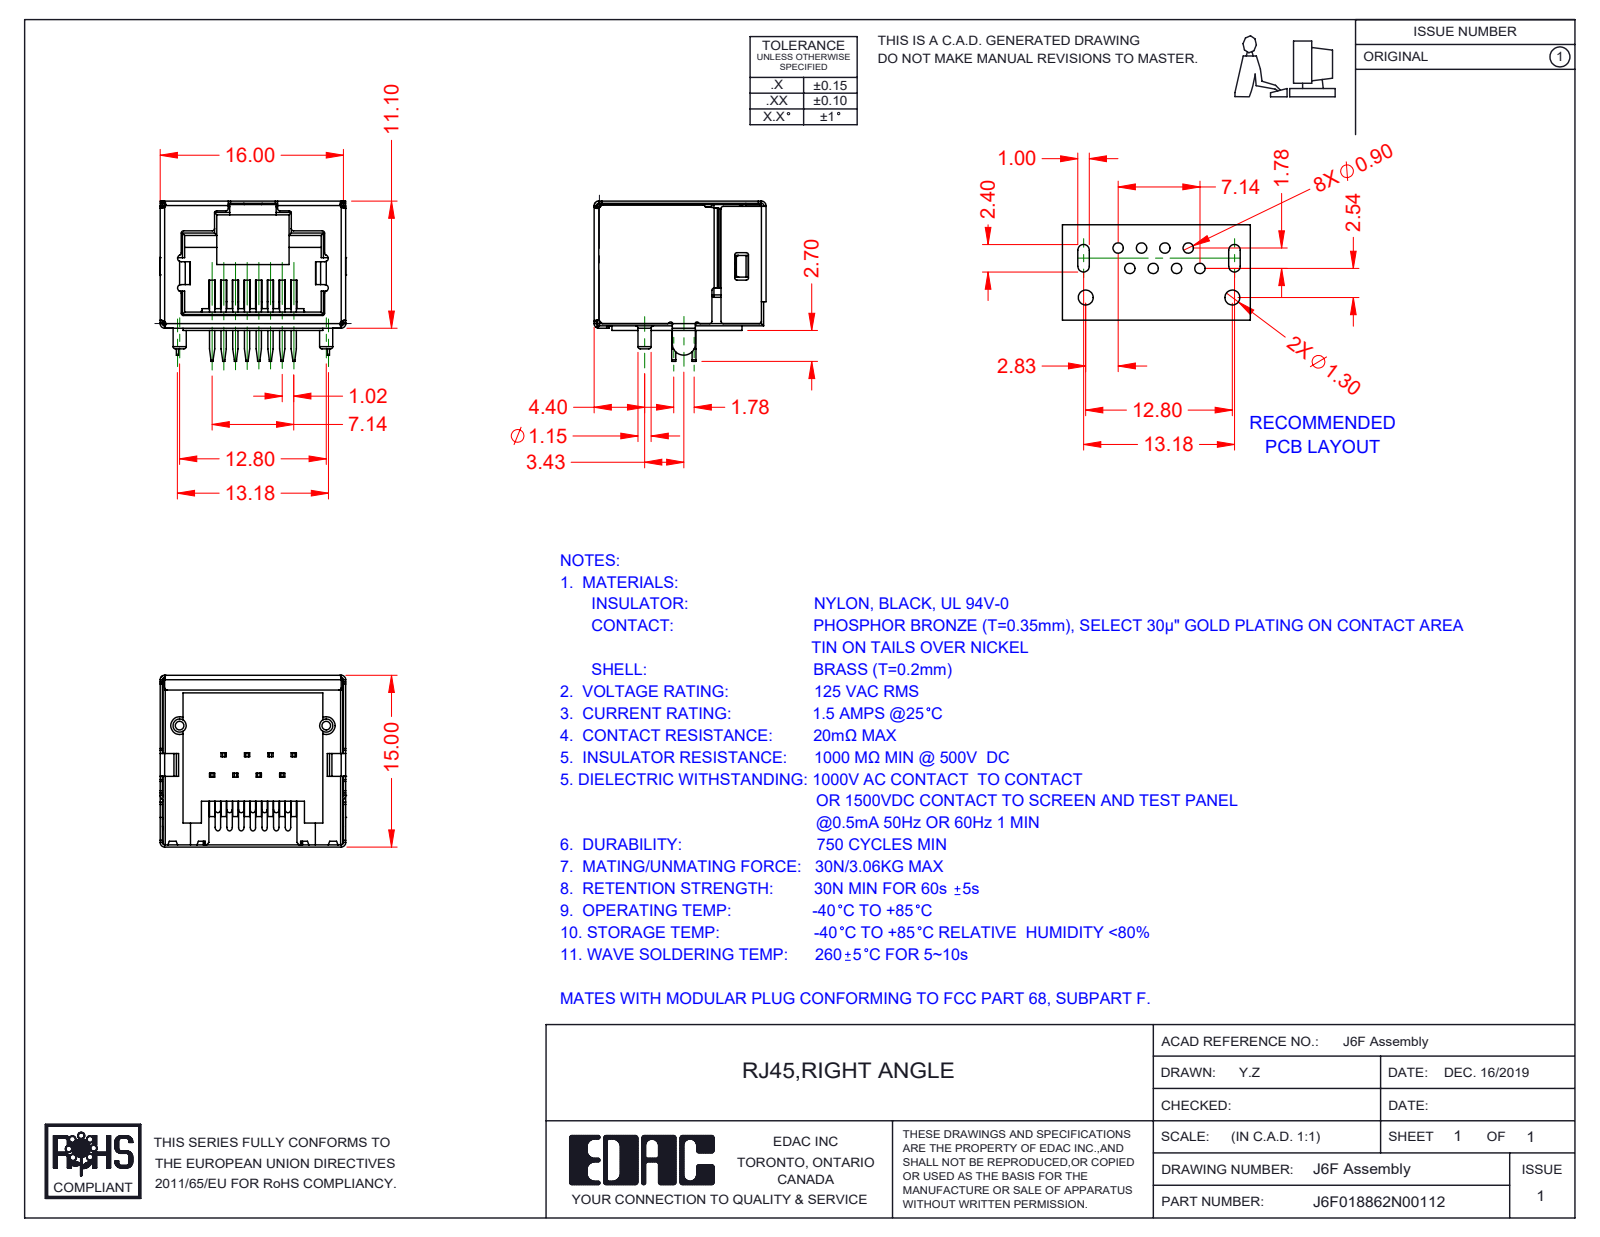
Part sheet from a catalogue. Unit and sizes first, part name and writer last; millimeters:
Units: millimetres
Overall size (bounding box): 16.2 × 15 × 14
Round bosses / shafts (diameter × count): ⌀1.15 ×2
Partial cylindrical surfaces — rounded edges, fillets, slot ends (radius × count): R0.2 ×77, R0.4 ×24, R0.3 ×20, R0.5 ×9, R0.23 ×7, R0.15 ×5, R0.1 ×4, R1 ×3
Main face-to-face distances: 15.75, 16, 15.95, 11, 15.7, 9.7, 11.1, 16.2, 15.8, 1.2
Volume: 1 336 mm³ · Surface area: 3 711 mm²
Bodies: 10 solids, 960 faces (695 planar, 223 cylindrical, 42 other)
Part name (STEP PRODUCT): 6F Shield; J6F018862N00112; 6F Insulator; 6F Contacts
STEP written by: SolidWorks 2016 (CONFIG_CONTROL_DESIGN)
